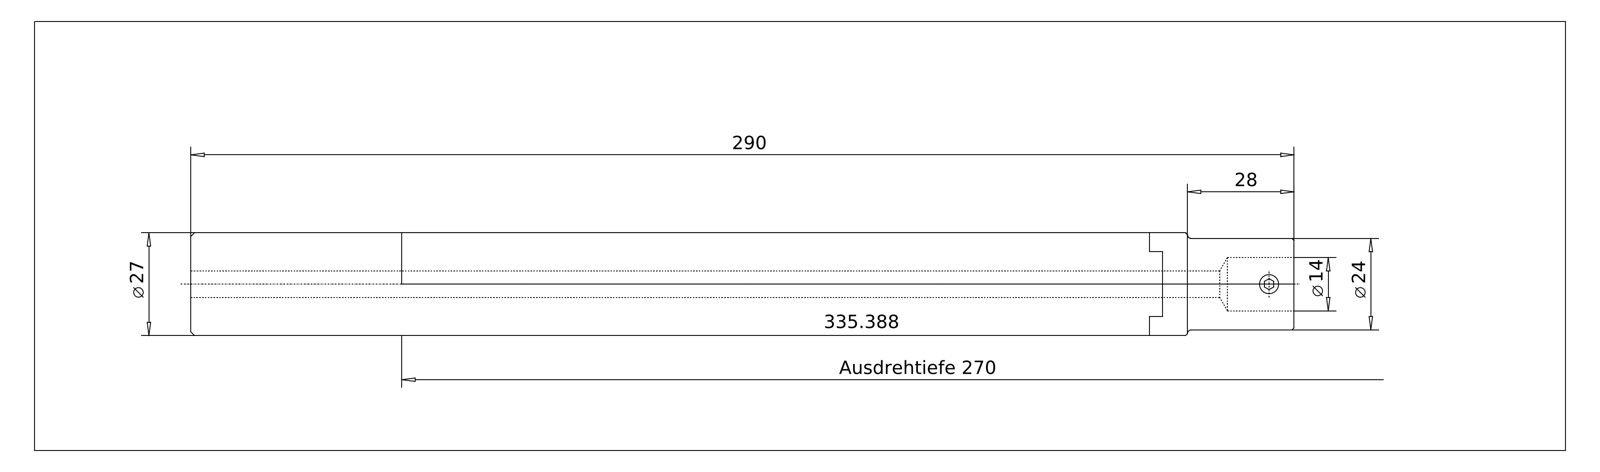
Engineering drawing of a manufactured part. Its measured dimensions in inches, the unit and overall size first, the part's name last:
Units: inches
Overall size (bounding box): 11.417 × 1.063 × 1.063
Round holes (diameter × count): ⌀0.176 ×1, ⌀0.205 ×1, ⌀0.276 ×1, ⌀0.551 ×1, ⌀0.571 ×1
Round bosses / shafts (diameter × count): ⌀1.063 ×1, ⌀0.945 ×1, ⌀0.197 ×1
Partial cylindrical surfaces — rounded edges, fillets, slot ends (radius × count): R0.079 ×2
Main face-to-face distances: 11.417, 0.464, 0.272, 11.146, 1.102, 0.831, 10.315, 0.256, 0.098, 0.098
Volume: 9.104 in³ · Surface area: 50.05 in²
Bodies: 2 solids, 77 faces (27 planar, 20 cylindrical, 30 other)
Part name (STEP PRODUCT): 335.388 Kaiser D27 X CK2 X 255HM|335.388 Kaiser D27 X CK2 X 255HM;NONE; 335.388 Kaiser D27 X CK2 X 255HM|690.432 Kaiser ETL M5 X 6,5 CK2;NONE
STEP written by: ACIS (automotive_design)
